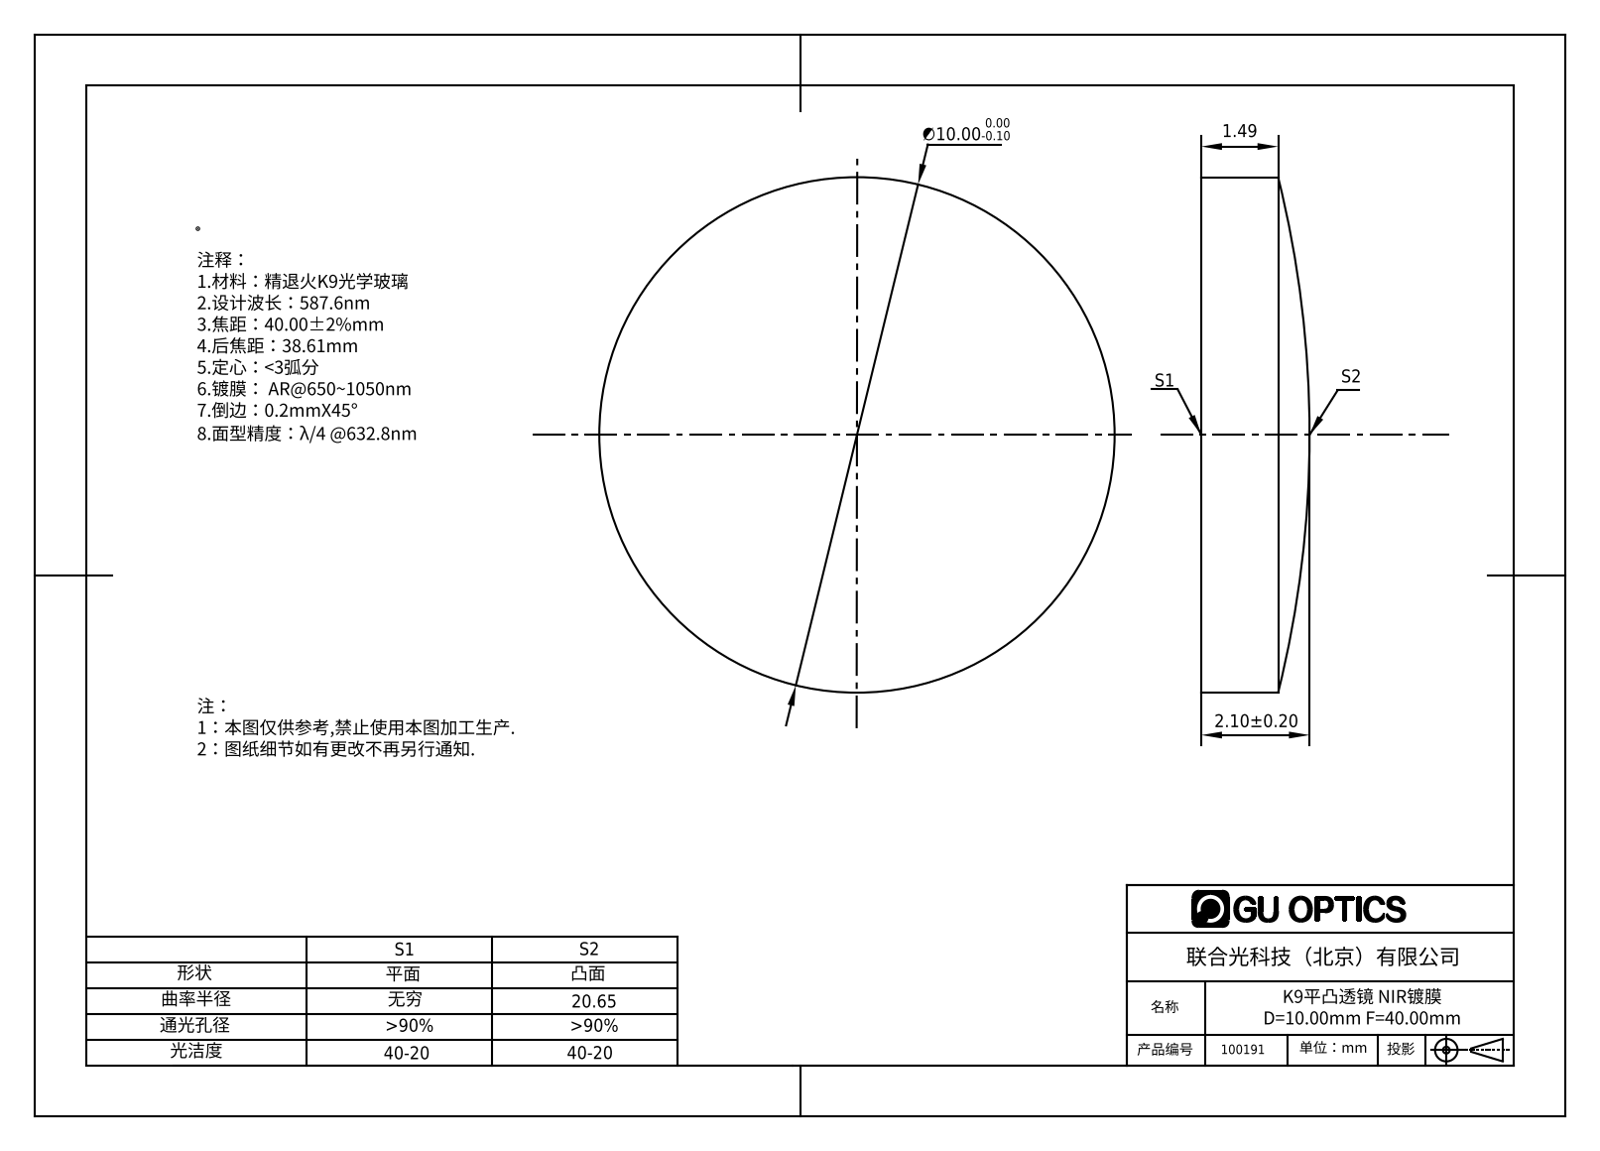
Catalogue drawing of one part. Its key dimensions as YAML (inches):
part_name: "100191"
step_written_by: "SolidWorks 2016 (AUTOMOTIVE_DESIGN)"
units: inches
bodies: {solids: 1, faces: 5, planar: 1, cylindrical: 2, other: 2}
overall_size: [0.394, 0.394, 0.083]
volume: 0.009
surface_area: 0.318
round_bosses_or_shafts:
  - {diameter: 0.394, count: 1}
